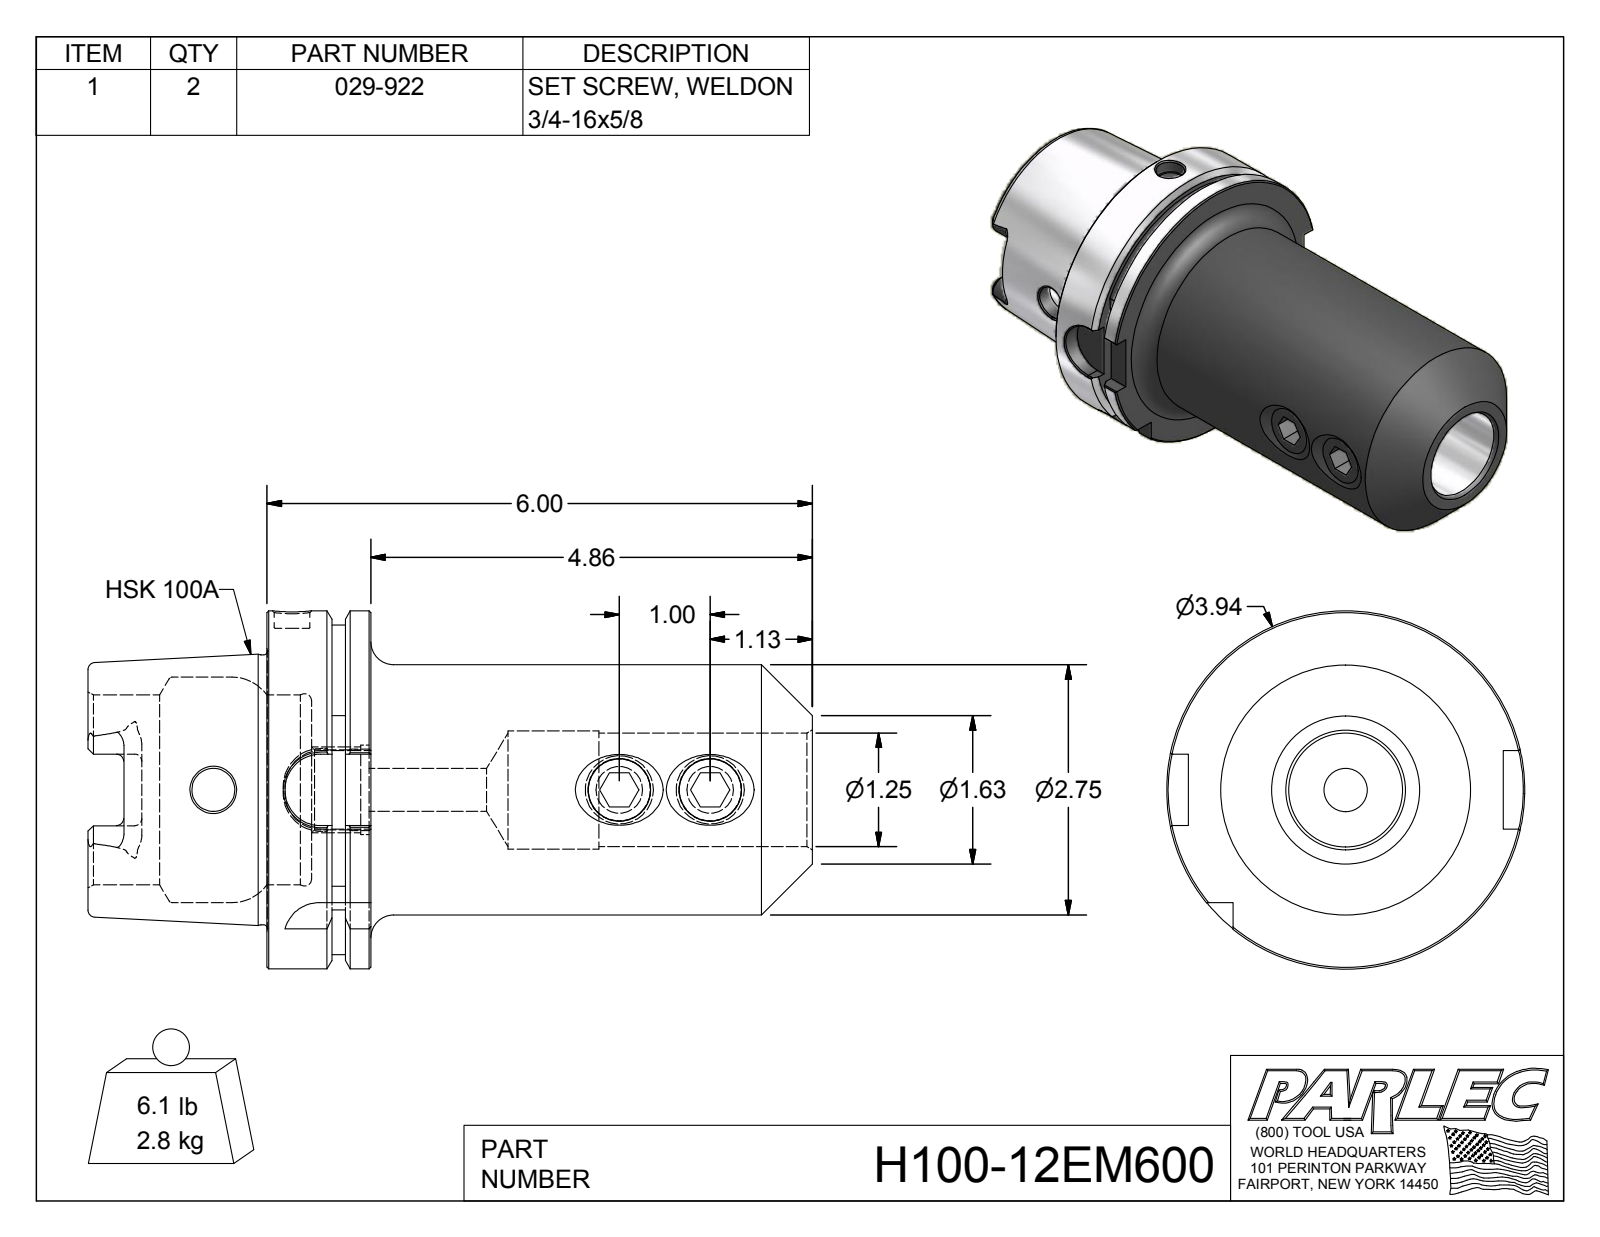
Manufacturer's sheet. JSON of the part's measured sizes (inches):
{"part_name": "H100-12EM600; 029-922", "step_written_by": "Autodesk Inventor 2012 (AUTOMOTIVE_DESIGN)", "units": "inches", "bodies": {"solids": 3, "faces": 154, "planar": 62, "cylindrical": 38, "other": 54}, "overall_size": [7.969, 3.937, 3.937], "volume_in3": 38.56, "surface_area_in2": 137.5, "round_holes": [[0.472, 2], [0.682, 2], [0.394, 1], [0.881, 1], [0.985, 1], [1.25, 1], [1.3, 1], [2.087, 1], [2.48, 1]], "round_bosses_or_shafts": [[0.75, 2], [3.937, 1], [2.967, 1], [2.75, 1]], "partial_cylinders_radius": [[0.079, 6], [0.192, 4], [0.394, 4], [1.811, 1]], "face_to_face_distances": [1.142, 0.492, 0.65, 1.969, 2.461, 3.11, 2.83, 0.861, 0.369, 0.28], "hole_center_spacings": [1, 4.466, 5.466]}
